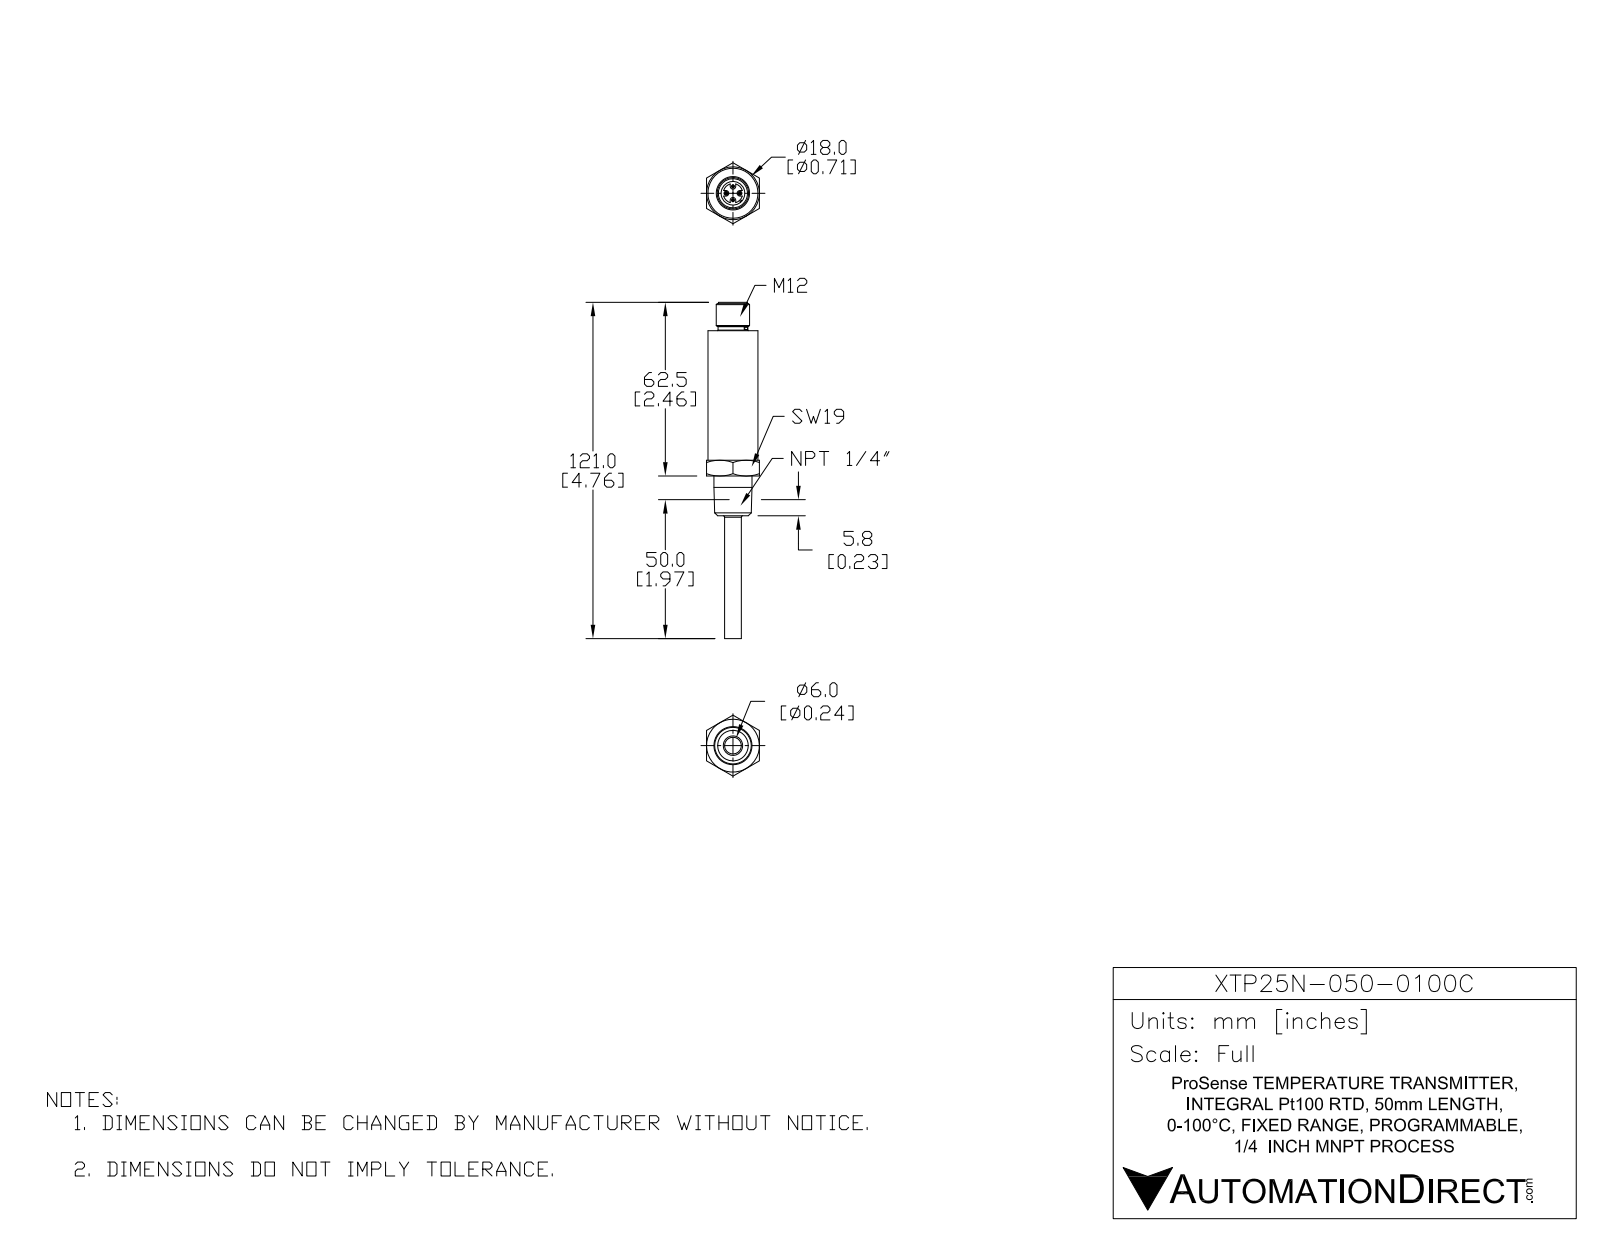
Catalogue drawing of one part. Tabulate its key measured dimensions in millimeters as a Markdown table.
| quantity | value |
| --- | --- |
| part name | XTP25N-050-0100C |
| STEP written by | SolidWorks 2015 (AUTOMOTIVE_DESIGN) |
| units | millimeters |
| bodies | 1 solid, 117 faces (43 planar, 34 cylindrical, 40 other) |
| overall size | 121 × 21.94 × 19 |
| volume | 17 233 mm³ |
| surface area | 6 004 mm² |
| round holes (diameter × count) | 4 × 1, 8.5 × 1 |
| round bosses / shafts (diameter × count) | 1.02 × 4, 18 × 1, 13.72 × 1, 12 × 1, 10.7 × 1, 10.5 × 1, 6 × 1 |
| partial cylindrical surfaces (radius × count) | 1 × 4, 3.5 × 1, 4.25 × 1 |
| main face-to-face distances | 19, 52.3, 14.3, 66.6, 20, 5.7, 46.6, 76.8, 62.5, 56.8 |
